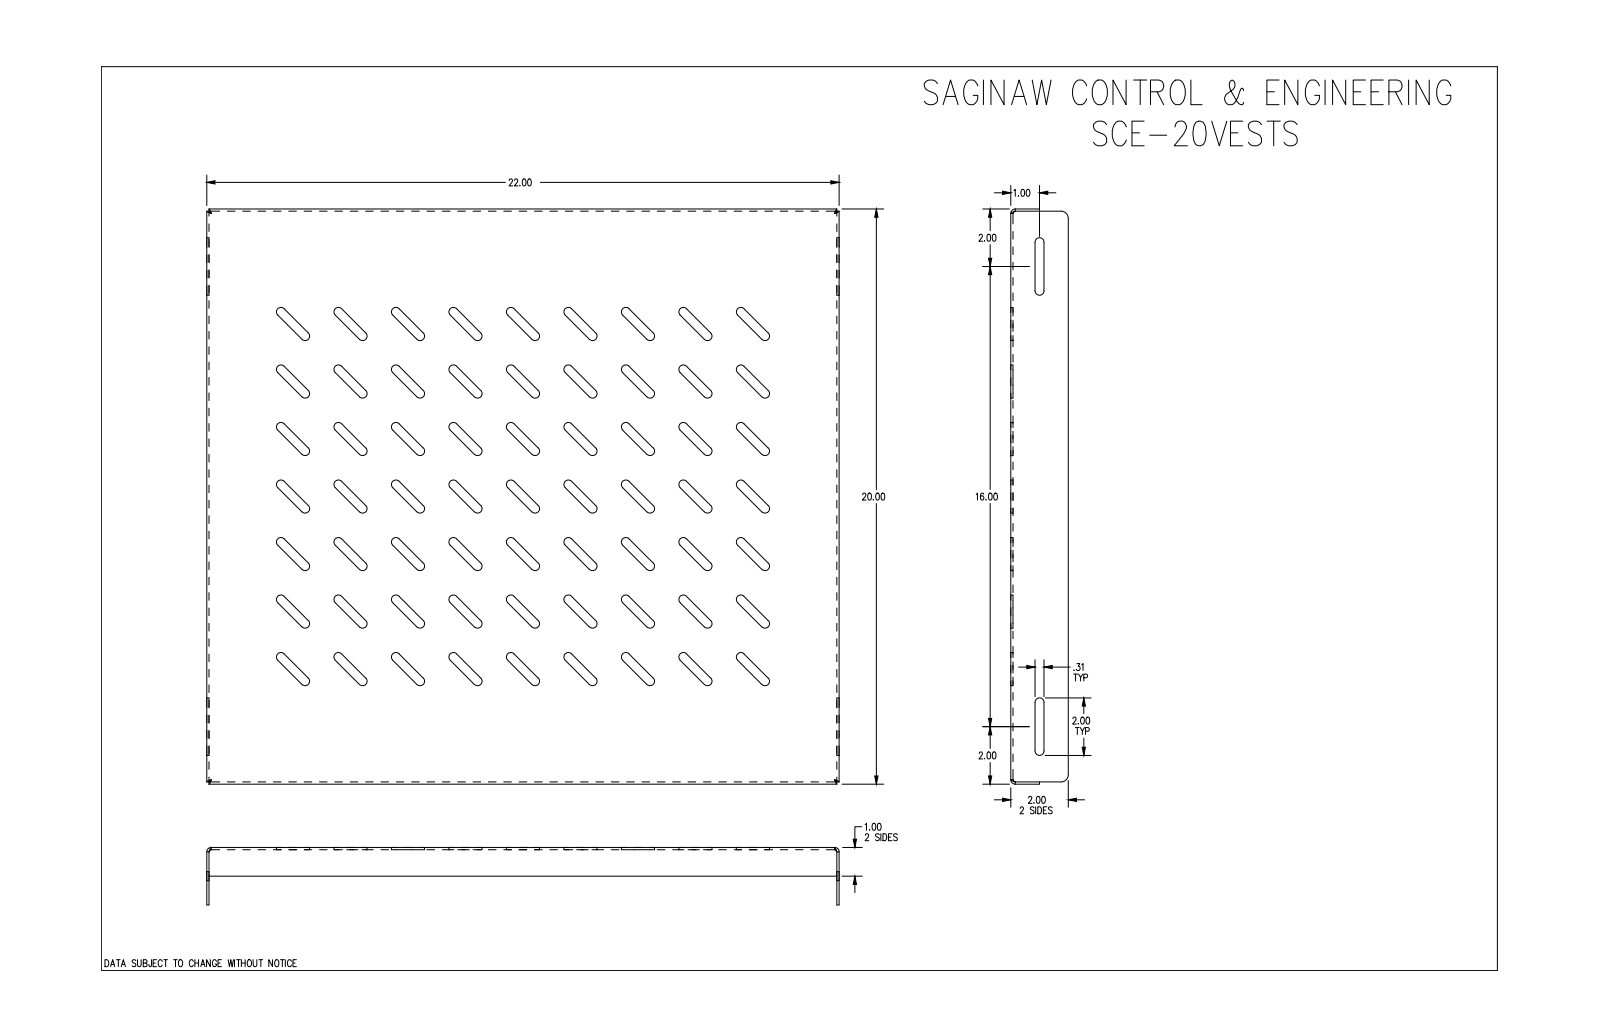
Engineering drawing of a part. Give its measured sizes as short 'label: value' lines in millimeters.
name: SCE-20VESTS
written by: SolidWorks 2019 (CONFIG_CONTROL_DESIGN)
unit: mm
bodies: 1 solid, 314 faces (156 planar, 150 cylindrical, 8 other)
size: 558.8 × 508 × 50.8
volume: 666 800 mm³; area: 689 700 mm²
rounds: 130× R4, 4× R2, 4× R4, 2× R0.5, 2× R6.4
face distances: 2, 556.8, 506, 554.8, 558.8, 504, 508, 71.8, 25.4, 143.7
